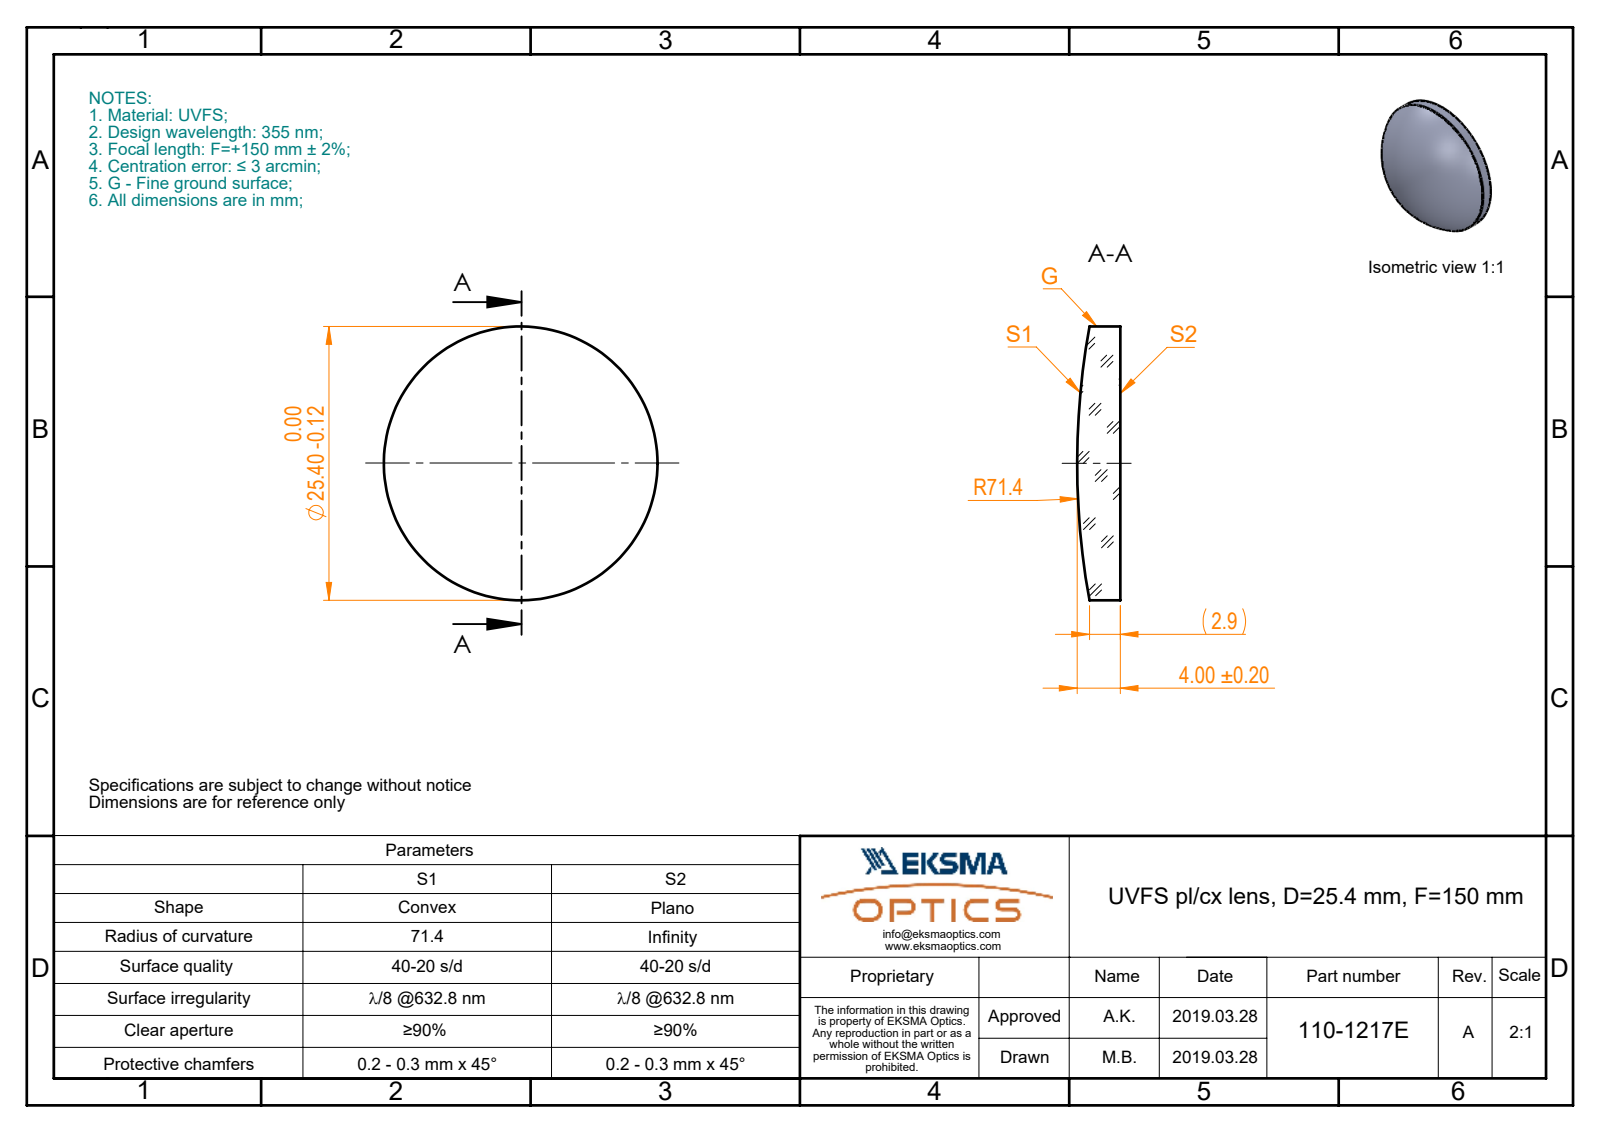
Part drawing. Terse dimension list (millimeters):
name: 110-1217E UVFS pl-cx 25.4 F150
written by: SolidWorks 2017 (CONFIG_CONTROL_DESIGN)
unit: mm
bodies: 1 solid, 5 faces (1 planar, 2 cylindrical, 2 other)
size: 25.4 × 25.4 × 4
volume: 1 739 mm³; area: 1 246 mm²
bosses: 1× ⌀25.4
